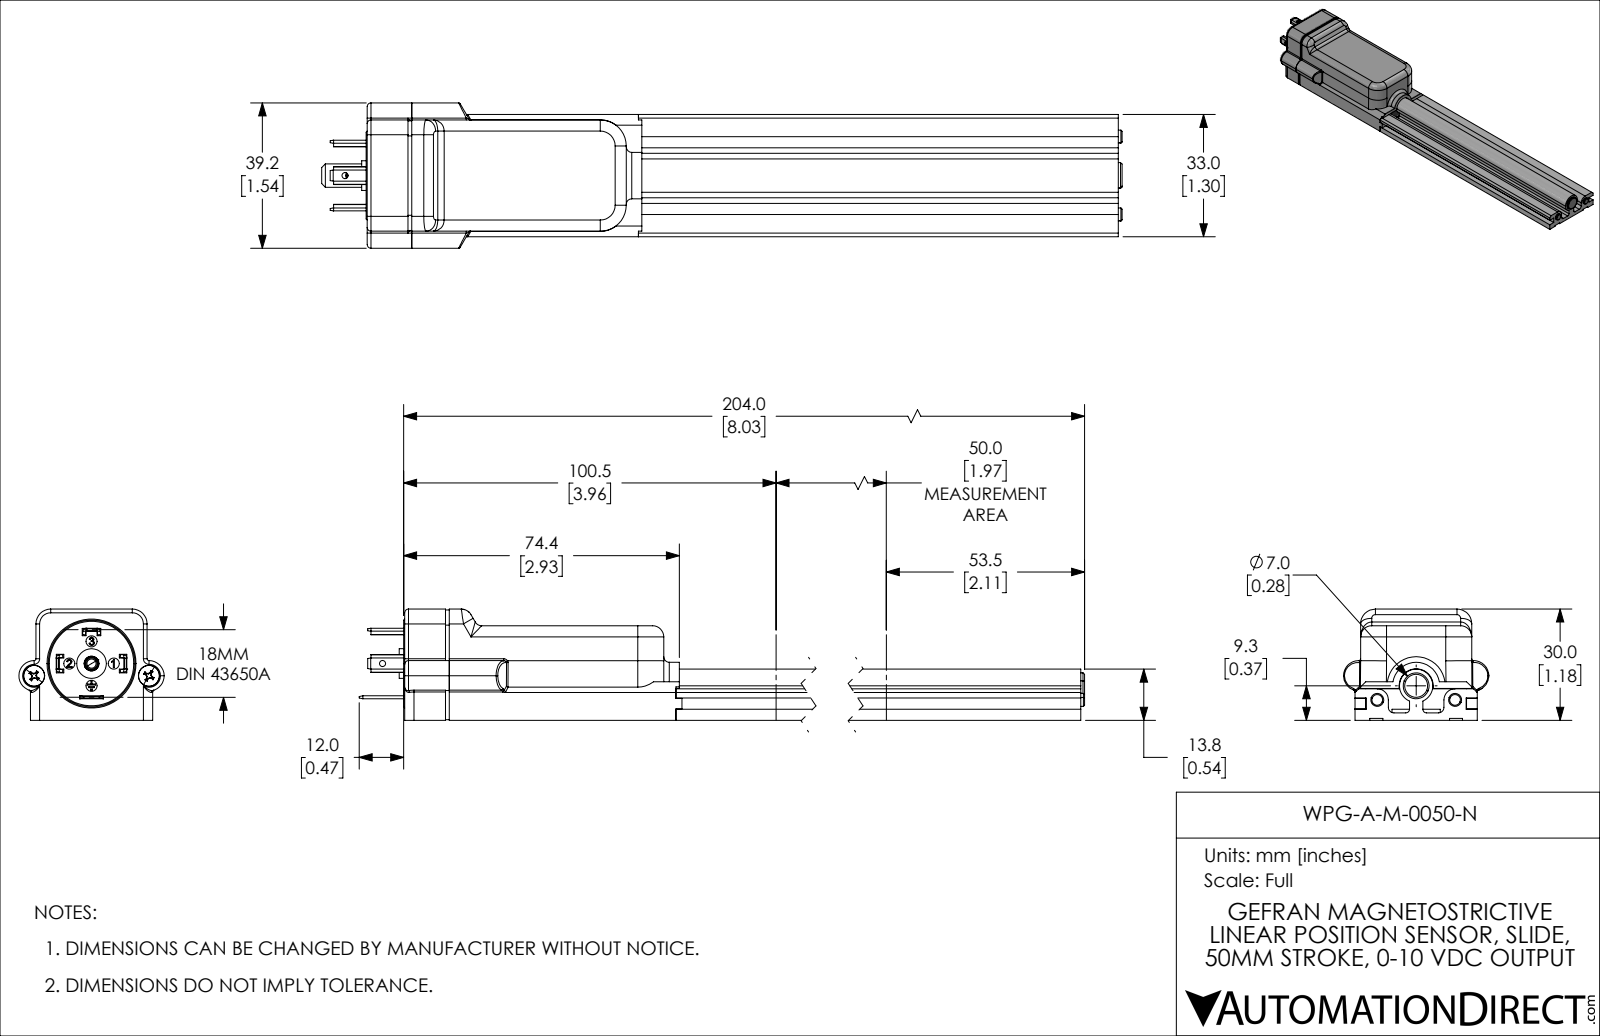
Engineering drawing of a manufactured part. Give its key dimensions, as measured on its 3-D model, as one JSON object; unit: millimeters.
{"part_name": "WPG-A-M-0050-N", "step_written_by": "SolidWorks 2021 (CONFIG_CONTROL_DESIGN)", "units": "millimeters", "bodies": {"solids": 15, "faces": 775, "planar": 373, "cylindrical": 203, "other": 199}, "overall_size": [216, 39.2, 30], "volume_mm3": 90264, "surface_area_mm2": 34665, "round_holes": [[3, 5], [1.5, 2], [1.65, 2], [3.2, 2], [5.7, 2], [1.6, 1], [2.5, 1], [4, 1]], "round_bosses_or_shafts": [[5.6, 2], [3.5, 2], [2.9, 2], [2.85, 2], [2.18, 2], [9, 1], [8, 1], [7, 1]], "partial_cylinders_radius": [[0.5, 8], [3, 8], [0.85, 6], [1, 5], [0.8, 4], [1.5, 4], [4.1, 4], [7, 4]], "face_to_face_distances": [1, 1.5, 3, 2.5, 5.5, 30, 6, 22.5, 8.5, 25.5], "hole_center_spacings": [6, 8.49, 10.06, 12, 12.3, 15.73, 15.85, 18.08]}
